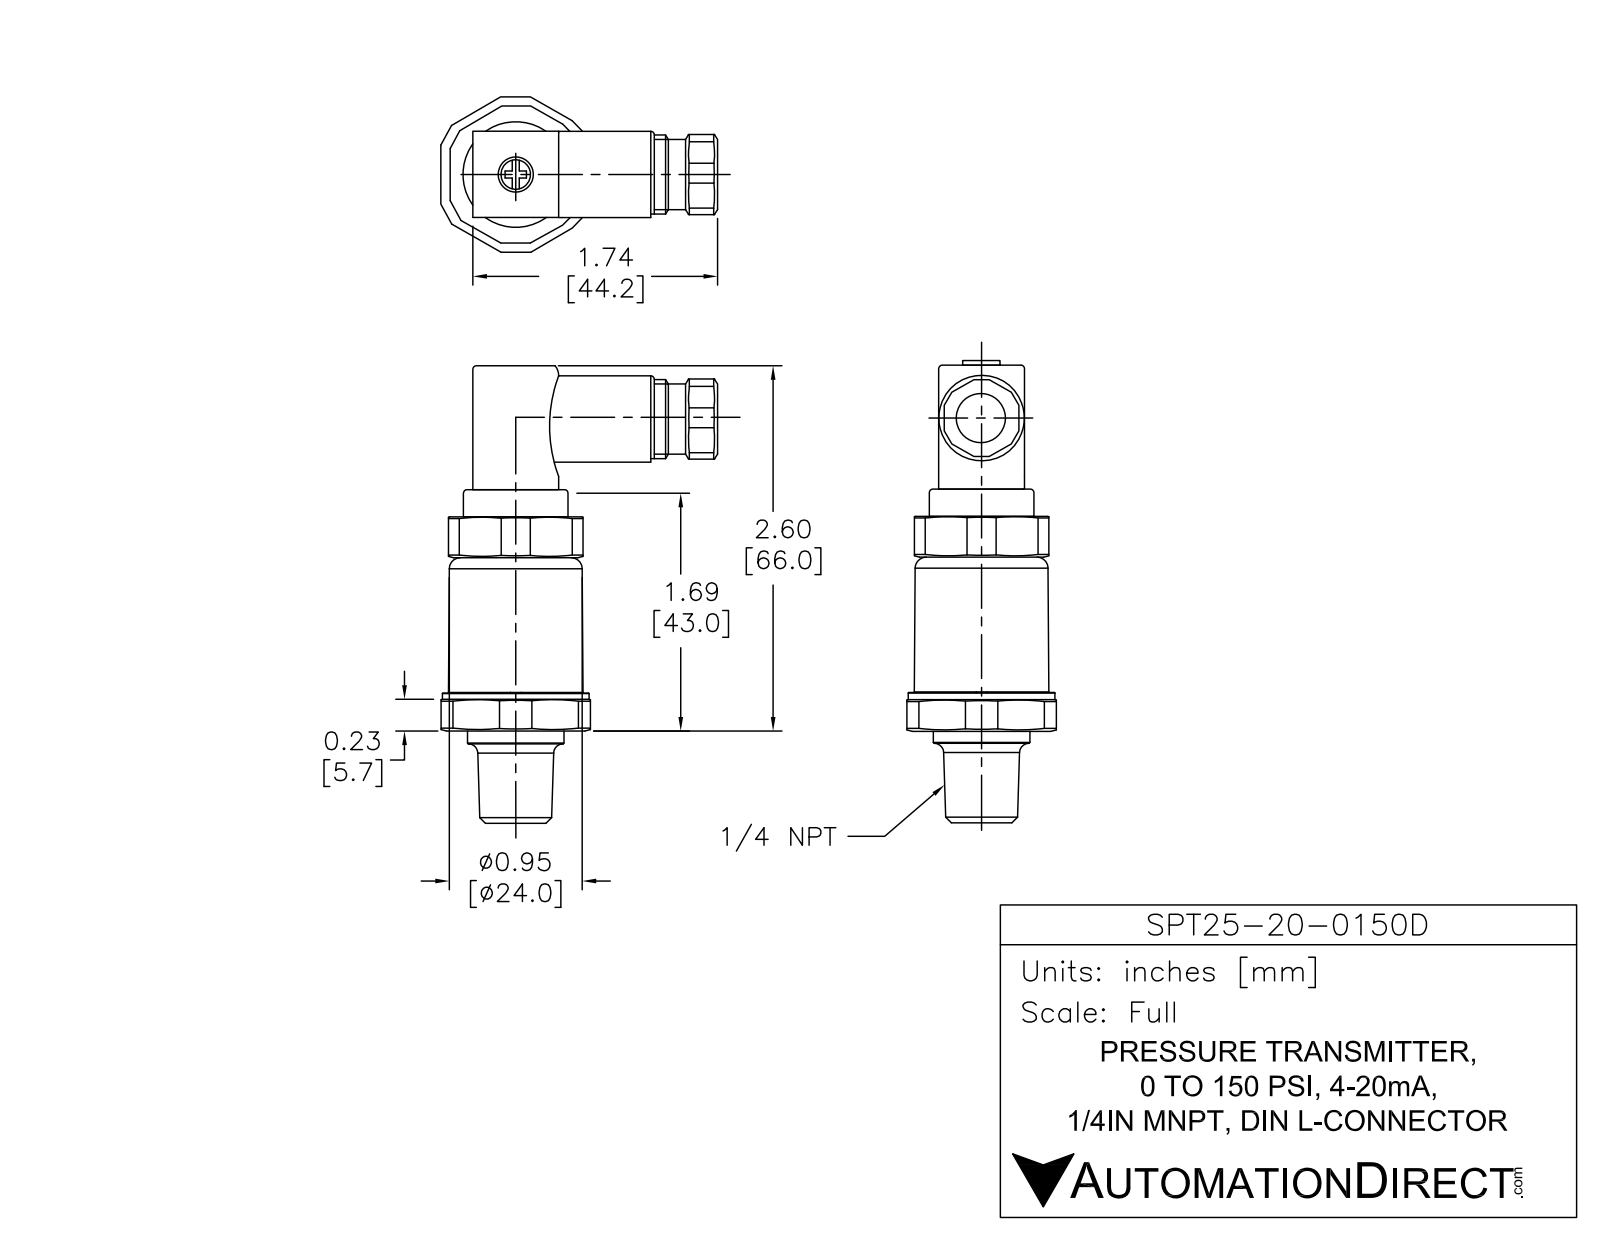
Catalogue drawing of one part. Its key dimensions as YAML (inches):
part_name: "SPT25-20-0150D"
step_written_by: "SolidWorks 2011 (AUTOMOTIVE_DESIGN)"
units: inches
bodies: {solids: 5, faces: 170, planar: 96, cylindrical: 64, other: 10}
overall_size: [3.199, 1.496, 1.406]
volume: 1.703
surface_area: 15.71
round_holes:
  - {diameter: 0.039, count: 1}
  - {diameter: 0.13, count: 1}
  - {diameter: 0.276, count: 1}
  - {diameter: 0.315, count: 1}
round_bosses_or_shafts:
  - {diameter: 1.053, count: 1}
  - {diameter: 0.945, count: 1}
  - {diameter: 0.689, count: 1}
  - {diameter: 0.591, count: 1}
  - {diameter: 0.551, count: 1}
  - {diameter: 0.433, count: 1}
partial_cylinders:
  - {radius: 0.059, count: 8}
  - {radius: 0.045, count: 4}
  - {radius: 0.089, count: 4}
  - {radius: 0.079, count: 3}
  - {radius: 0.045, count: 1}
  - {radius: 0.046, count: 1}
  - {radius: 0.571, count: 1}
face_to_face_distances: [0.059, 1.161, 1.22, 0.62, 0.014, 0.606, 0.266, 1.486, 1.427, 0.197]
hole_center_spacings: [0.052]
